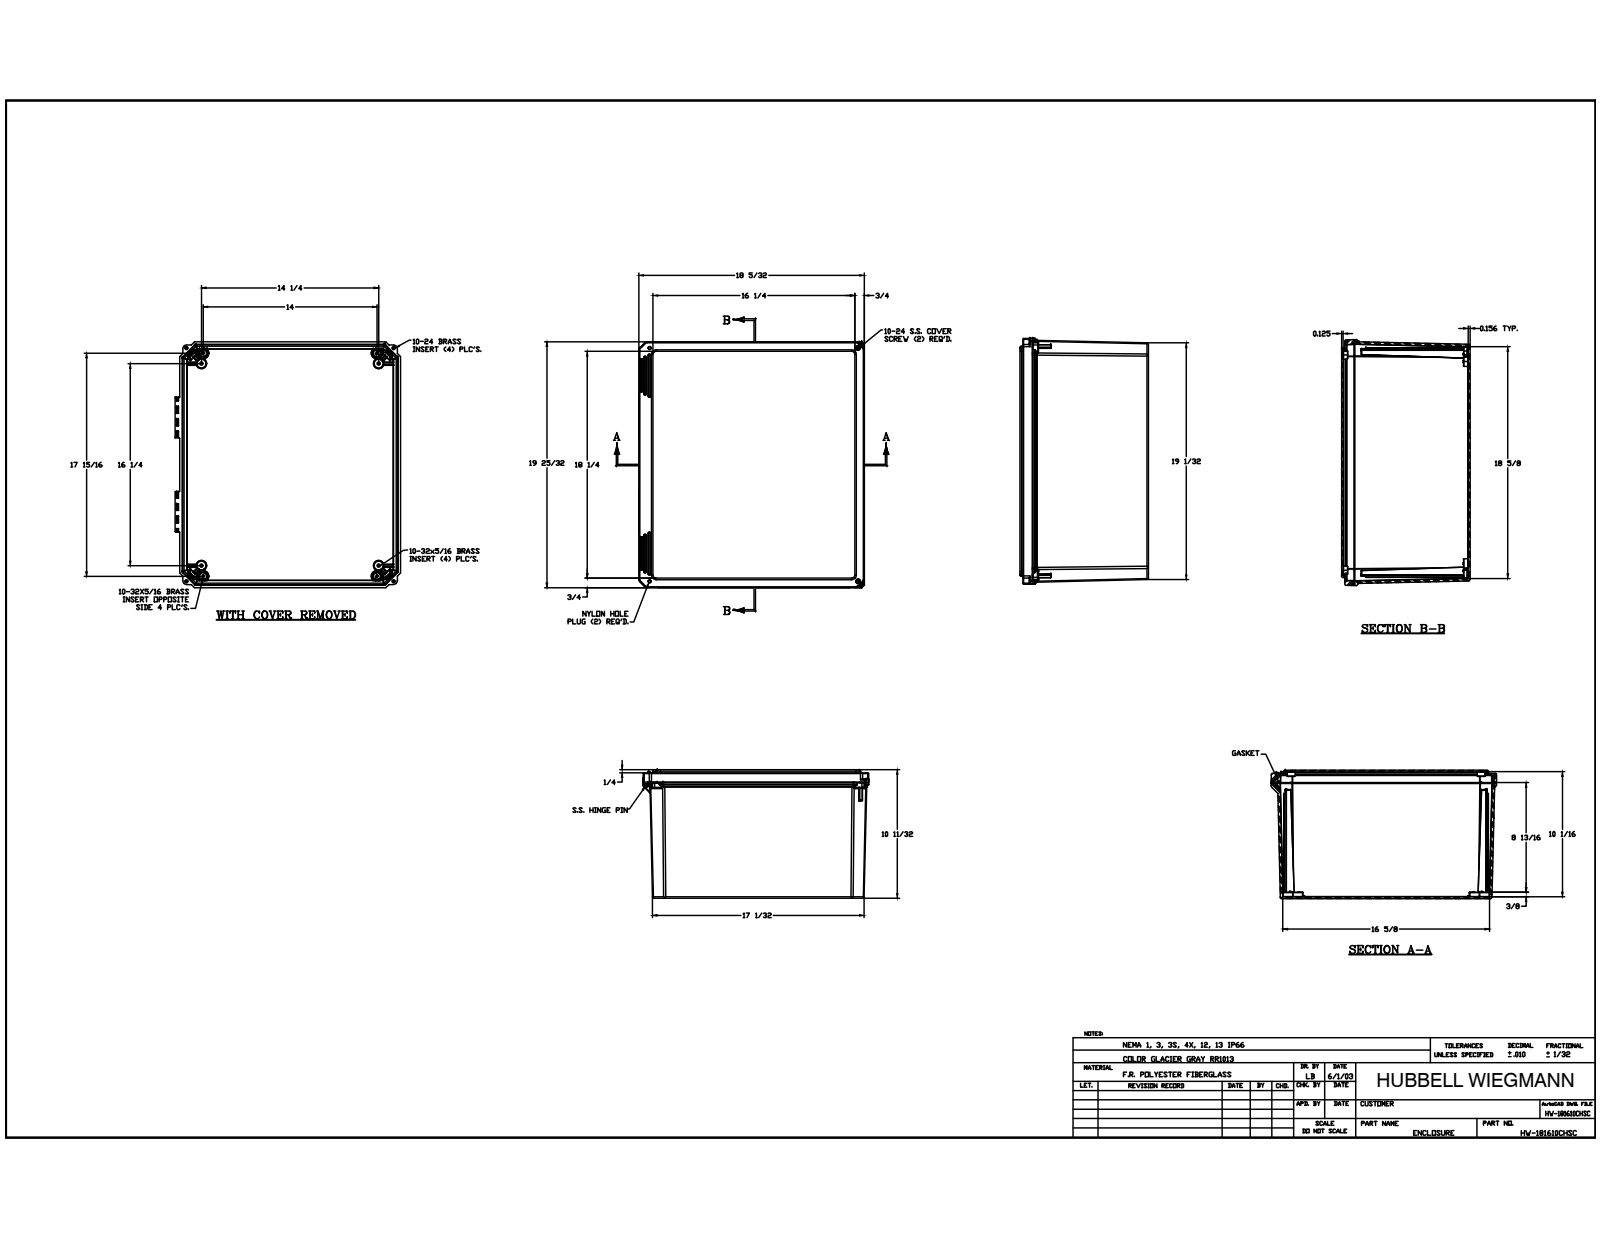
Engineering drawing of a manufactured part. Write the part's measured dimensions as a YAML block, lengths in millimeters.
part_name: "DS181610BOX; BRASS INSERT-(; BRASS INSERT-(_1; BRASS INSERT-(_2 (+8 more)"
step_written_by: "Autodesk Inventor 2014 (AUTOMOTIVE_DESIGN)"
units: millimeters
bodies: {solids: 29, faces: 2416, planar: 804, cylindrical: 922, other: 690}
overall_size: [502.21, 460.94, 262.67]
volume: 4256000
surface_area: 1908000
round_holes:
  - {diameter: 3.96, count: 16}
  - {diameter: 3.86, count: 8}
  - {diameter: 6.4, count: 4}
  - {diameter: 6.43, count: 4}
  - {diameter: 3.81, count: 2}
  - {diameter: 5.56, count: 2}
  - {diameter: 5.77, count: 2}
  - {diameter: 7.94, count: 2}
  - {diameter: 3.48, count: 1}
round_bosses_or_shafts:
  - {diameter: 6.25, count: 16}
  - {diameter: 11.43, count: 2}
  - {diameter: 11.05, count: 2}
  - {diameter: 5.3, count: 2}
  - {diameter: 5.05, count: 2}
  - {diameter: 3.43, count: 1}
partial_cylinders:
  - {radius: 0.25, count: 205}
  - {radius: 0.51, count: 111}
  - {radius: 0.13, count: 88}
  - {radius: 0.76, count: 39}
  - {radius: 1.59, count: 26}
  - {radius: 0.76, count: 24}
  - {radius: 2.29, count: 24}
  - {radius: 2.44, count: 24}
face_to_face_distances: [3.17, 3.96, 258.71, 262.67, 5.13, 5.08, 259.5, 255.54, 6.35, 3.18]
hole_center_spacings: [45.28, 36.73, 359.41, 395.27, 594.16, 608.39, 21.74, 361.94]
